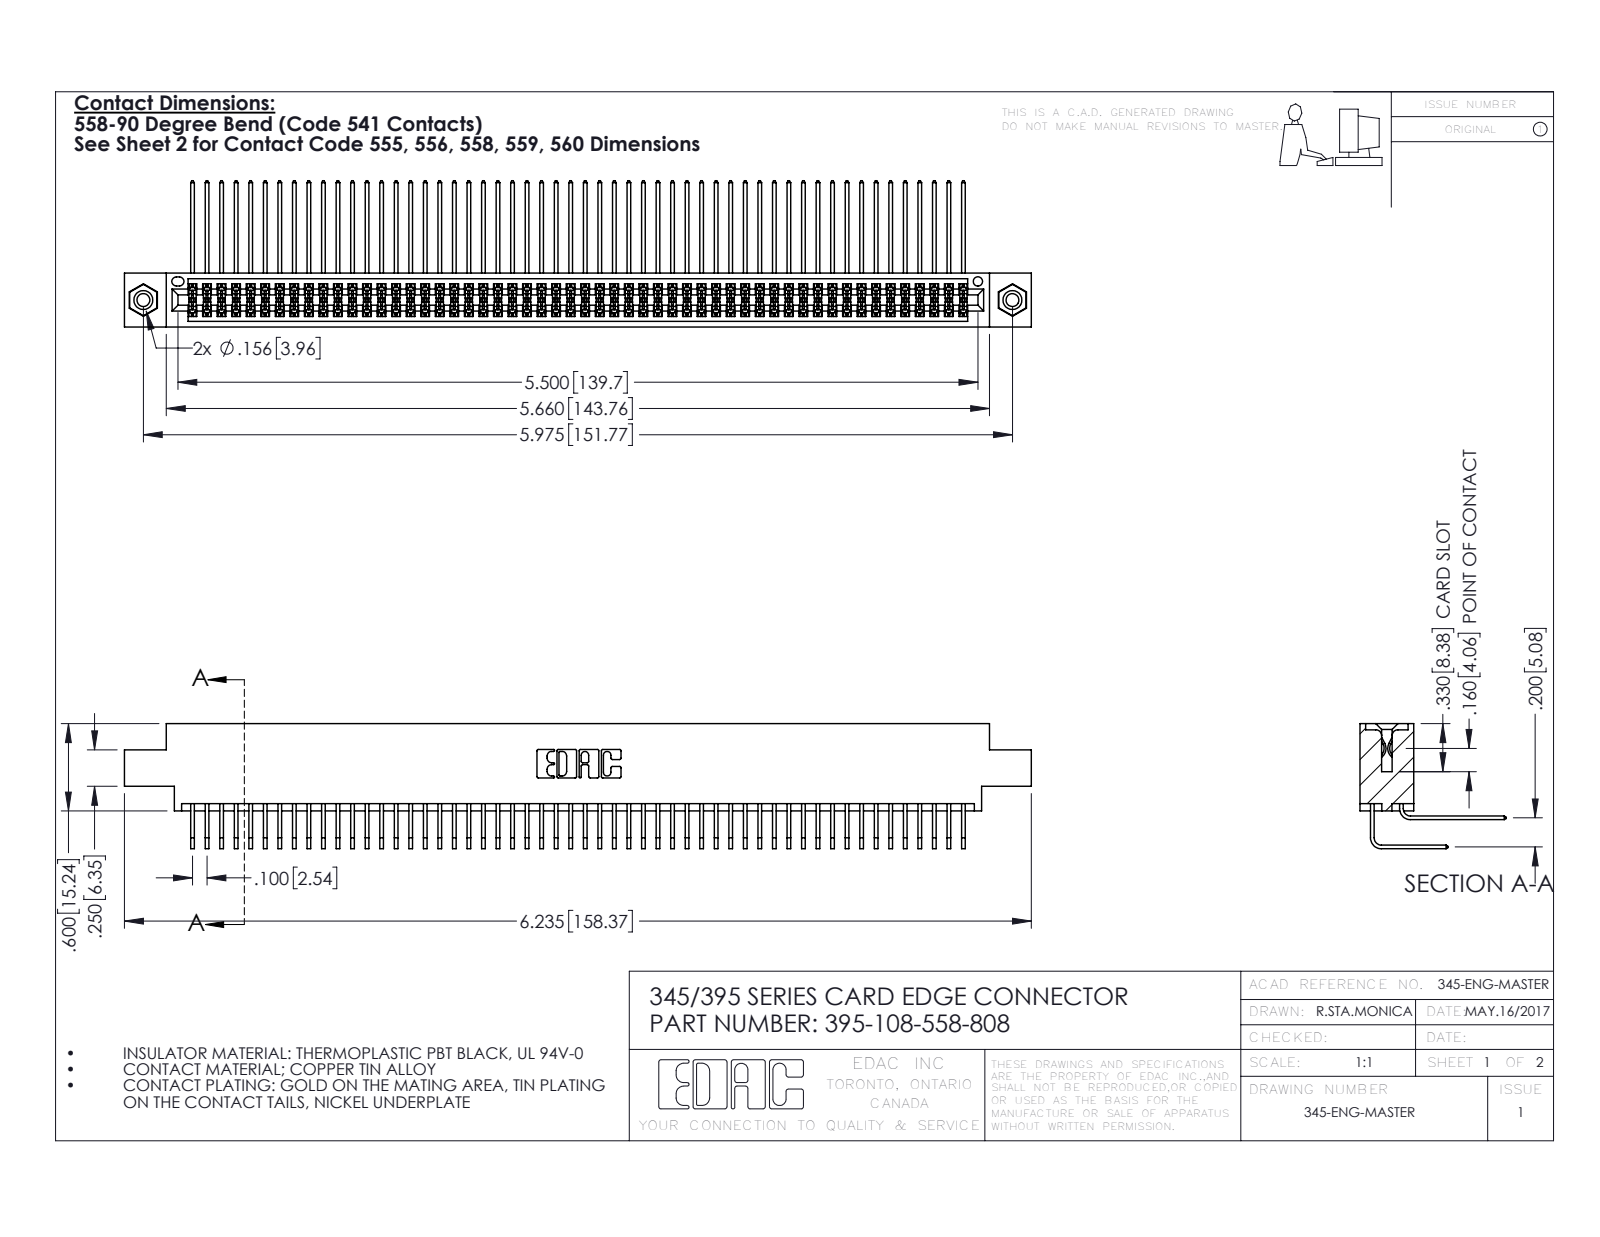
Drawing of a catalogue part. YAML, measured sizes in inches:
part_name: "345 Part_0.170 Offset - 0.156 Dia-TI; 395-108-558-808; 345-250-001_345-250-003-102; 345-292-001_558 559 Tail - 1 (+1 more)"
step_written_by: "SolidWorks 2016 (CONFIG_CONTROL_DESIGN)"
units: inches
bodies: {solids: 111, faces: 5806, planar: 3896, cylindrical: 1894, other: 16}
overall_size: [6.235, 1.005, 0.859]
volume: 0.976
surface_area: 41.8
round_holes:
  - {diameter: 0.089, count: 2}
  - {diameter: 0.125, count: 2}
  - {diameter: 0.156, count: 2}
  - {diameter: 0.064, count: 1}
round_bosses_or_shafts:
  - {diameter: 0.155, count: 2}
partial_cylinders:
  - {radius: 0.006, count: 162}
  - {radius: 0.01, count: 22}
  - {radius: 0.007, count: 6}
  - {radius: 0.031, count: 6}
  - {radius: 0.026, count: 3}
  - {radius: 0.014, count: 2}
  - {radius: 0.019, count: 2}
  - {radius: 0.022, count: 2}
face_to_face_distances: [0.072, 0.298, 0.2, 0.37, 0.098, 0.272, 0.025, 0.225, 0.175, 0.025]
hole_center_spacings: [0.27, 5.739, 5.975]
